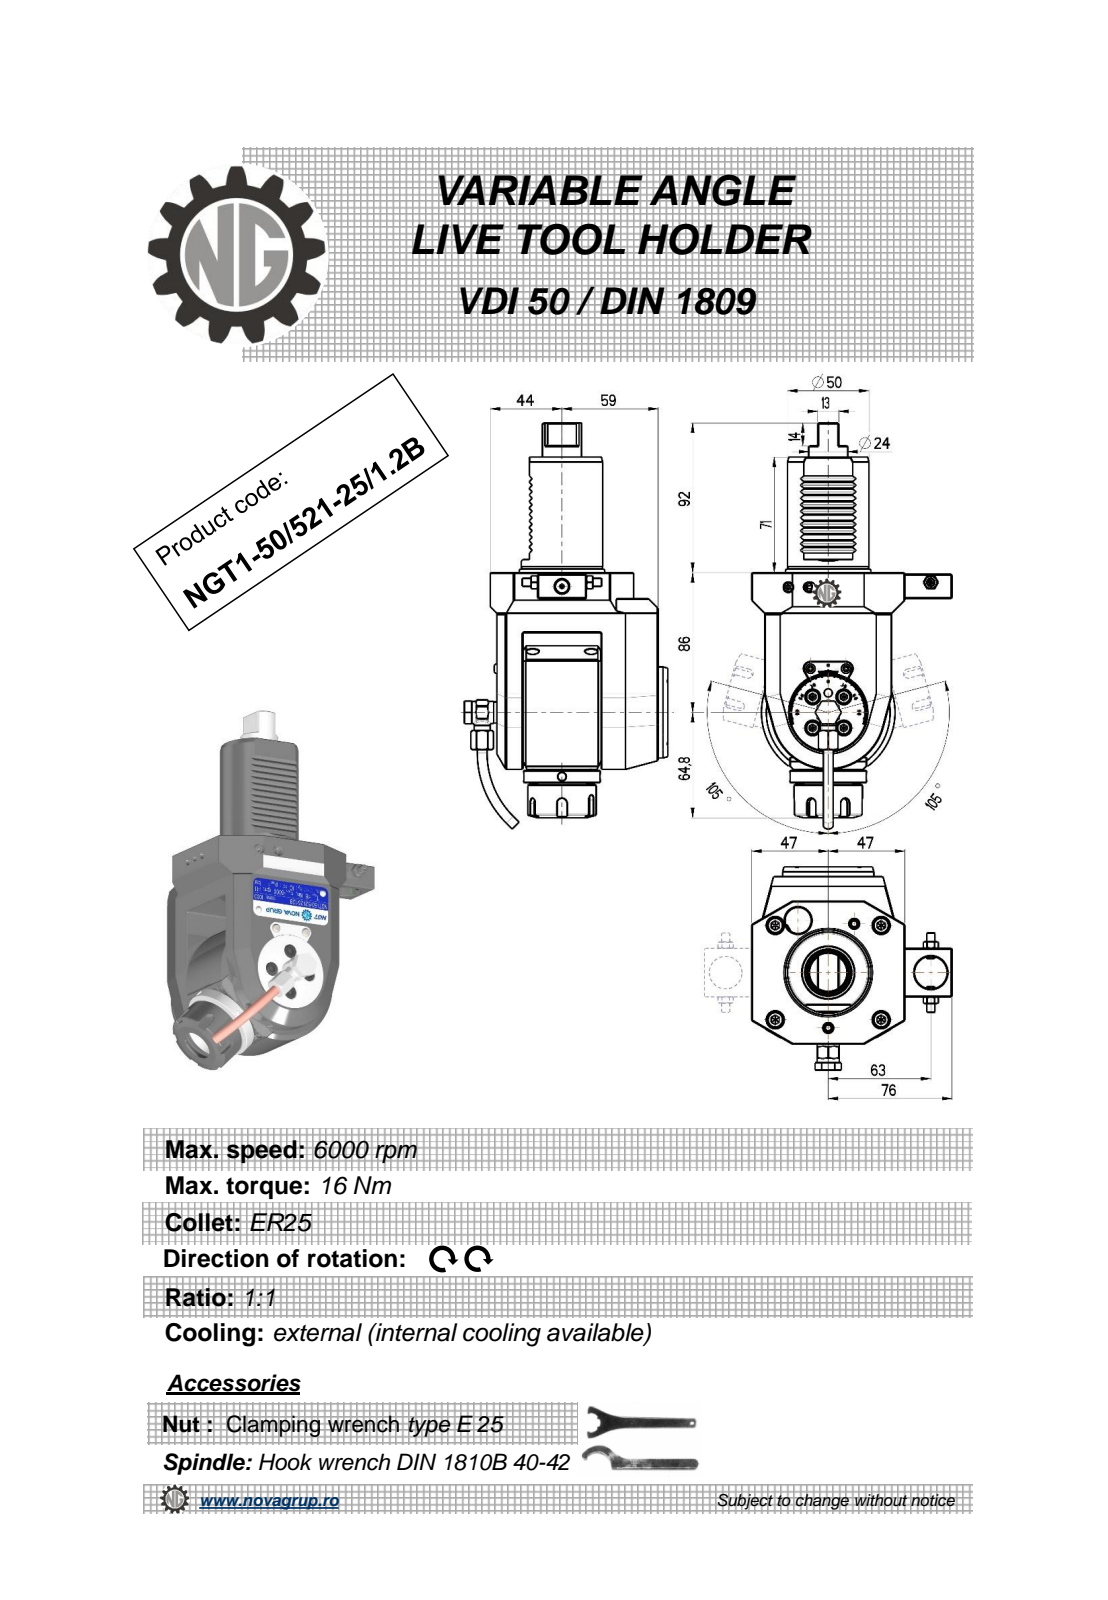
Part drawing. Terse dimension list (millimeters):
name: NGT1_50_521_25_1_2B
written by: PRO/ENGINEER BY PARAMETRIC TECHNOLOGY CORPORATION, 2010280 (CONFIG_CONTROL_DESIGN)
unit: mm
bodies: 1 solid, 616 faces (269 planar, 146 cylindrical, 201 other)
size: 249.67 × 124.9 × 123
volume: 1 012 000 mm³; area: 90 875 mm²
holes: 5× ⌀4, 2× ⌀3.8, 2× ⌀5, 1× ⌀3, 1× ⌀6.2, 1× ⌀9, 1× ⌀9.5, 1× ⌀10, 1× ⌀11, 1× ⌀20, 1× ⌀20.3
bosses: 2× ⌀6, 2× ⌀5.7, 1× ⌀82, 1× ⌀56, 1× ⌀50, 1× ⌀47, 1× ⌀42, 1× ⌀35
rounds: 12× R0.26, 12× R0.3, 6× R0.16, 5× R3, 4× R0.5, 2× R0.8, 2× R1, 2× R10
face distances: 37, 99, 16, 8, 21, 6, 64, 105, 20, 35
hole spacings: 9, 117.3, 0.4, 18, 39.45, 49, 49.4, 63
